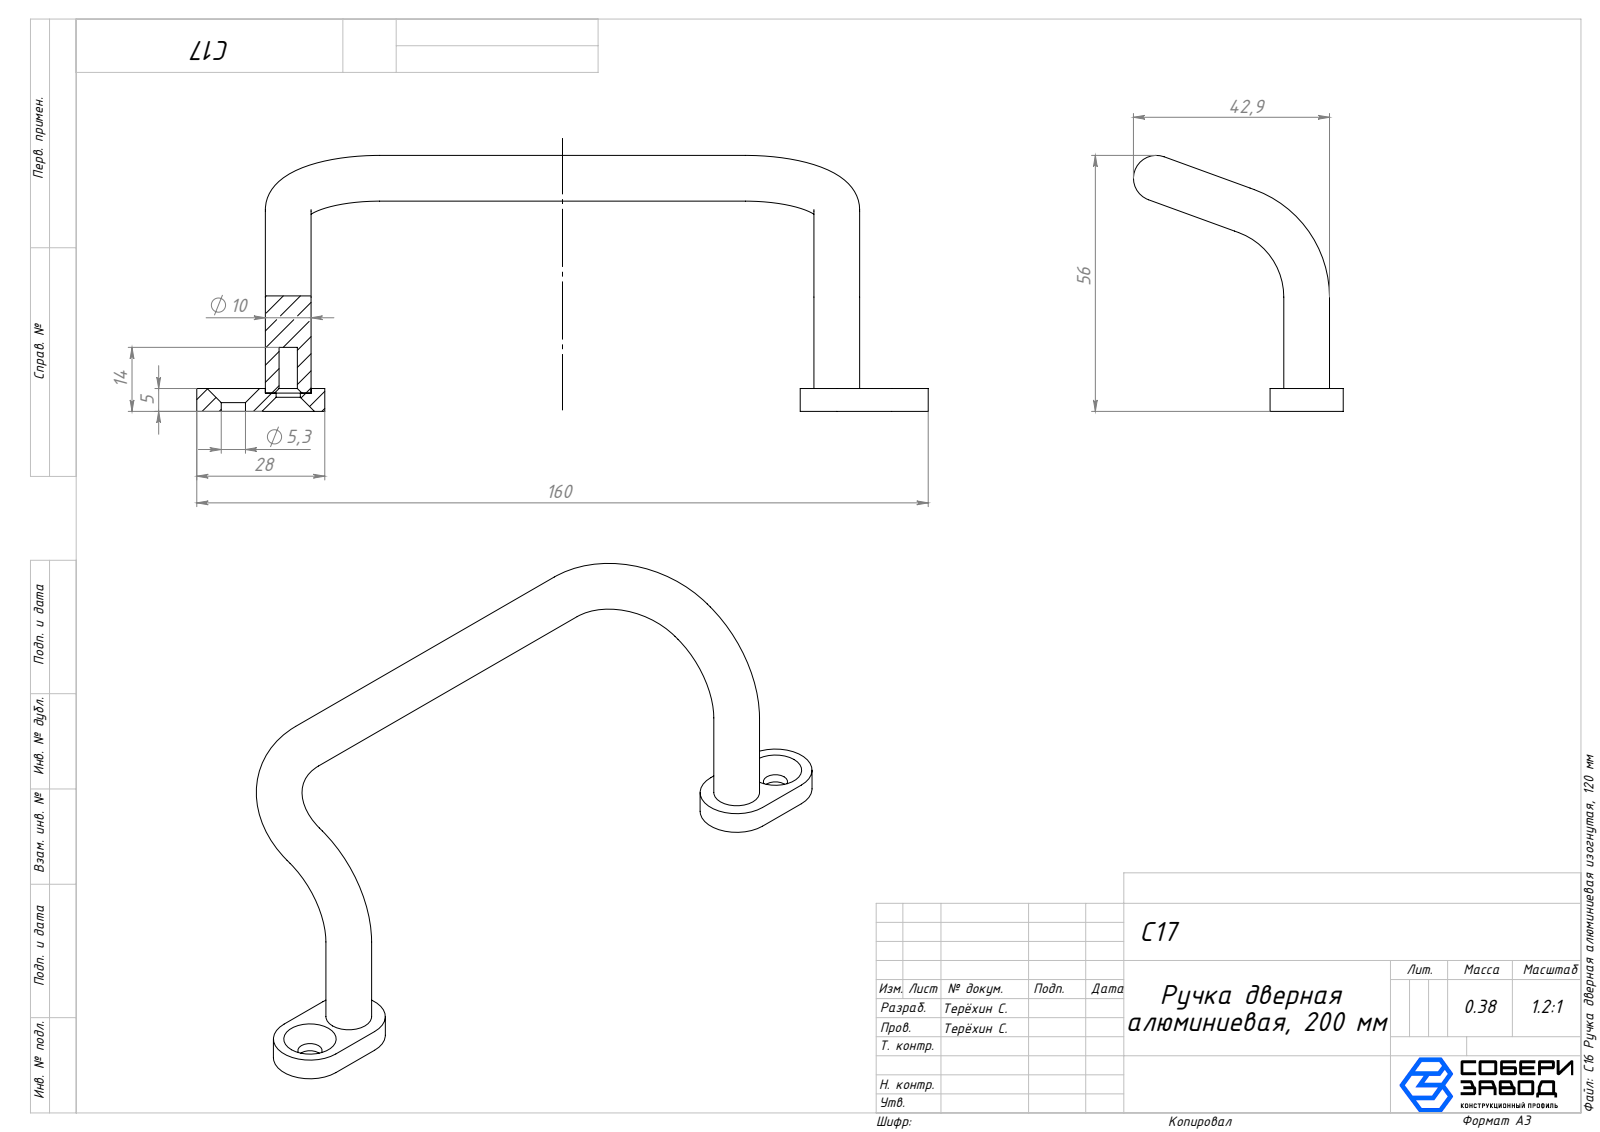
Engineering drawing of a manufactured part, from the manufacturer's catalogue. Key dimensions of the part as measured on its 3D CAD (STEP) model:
Part name (STEP PRODUCT): С16 Ручка_00; Сборка1; socket countersunk head screw_din_DIN 7991 - M5 x 10 --- 4.8N; С16 Крепление ручки_00 (+1 more)
STEP written by: SolidWorks 2025 (AUTOMOTIVE_DESIGN)
Units: millimetres
Bodies: 5 solids, 118 faces (42 planar, 40 cylindrical, 36 other)
Overall size (bounding box): 160 × 55.97 × 45.89
Volume: 21 692 mm³ · Surface area: 10 863 mm²
Round holes (diameter × count): ⌀5.3 ×4, ⌀4 ×2, ⌀10 ×2
Round bosses / shafts (diameter × count): ⌀10 ×3, ⌀9.64 ×2, ⌀5 ×2
Partial cylindrical surfaces — rounded edges, fillets, slot ends (radius × count): R8 ×4
Main face-to-face distances: 5, 4, 1, 3.57, 0.43, 4.57, 16, 10, 10.43, 6.43
Hole centre spacings: 12, 132, 120, 144
